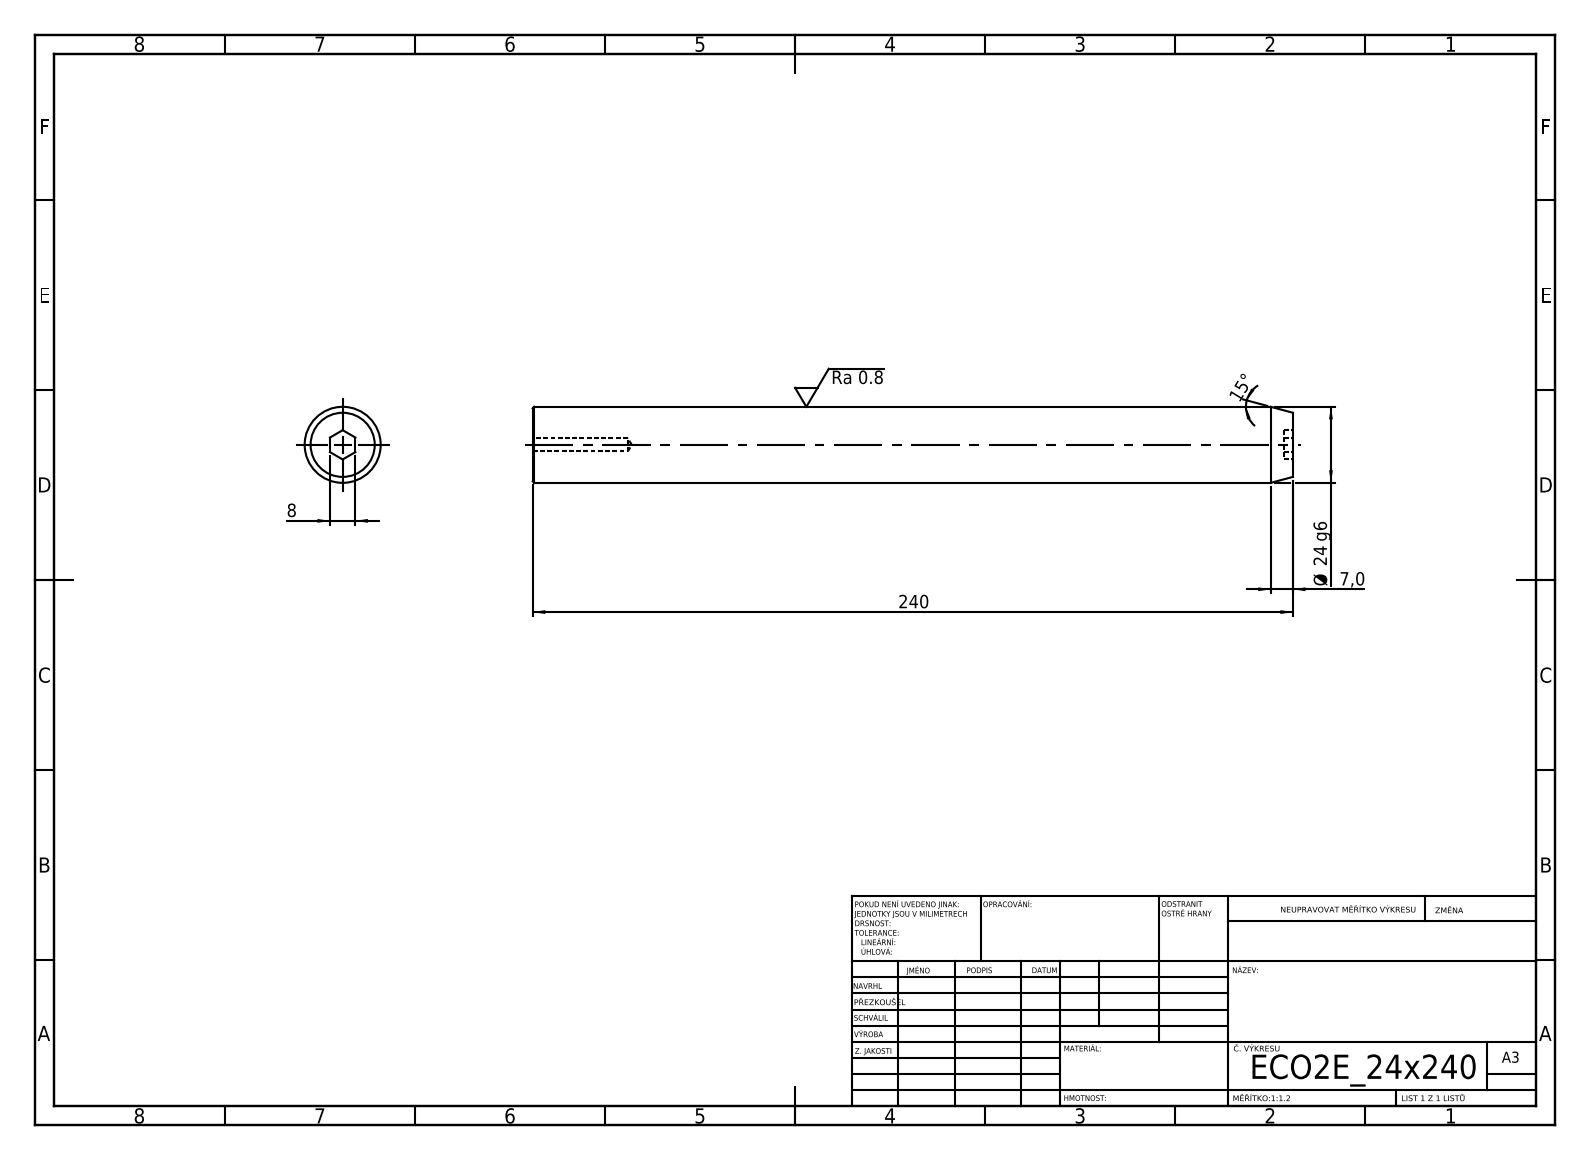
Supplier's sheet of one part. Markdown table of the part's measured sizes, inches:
| quantity | value |
| --- | --- |
| STEP written by | SolidWorks 2019 (CONFIG_CONTROL_DESIGN) |
| units | inches |
| bodies | 1 solid, 19 faces (9 planar, 4 cylindrical, 6 other) |
| overall size | 9.449 × 0.945 × 0.945 |
| volume | 6.561 in³ |
| surface area | 29.91 in² |
| round holes (diameter × count) | 0.165 × 1 |
| round bosses / shafts (diameter × count) | 0.945 × 1 |
| main face-to-face distances | 9.449, 0.11, 9.339, 0.315 |
